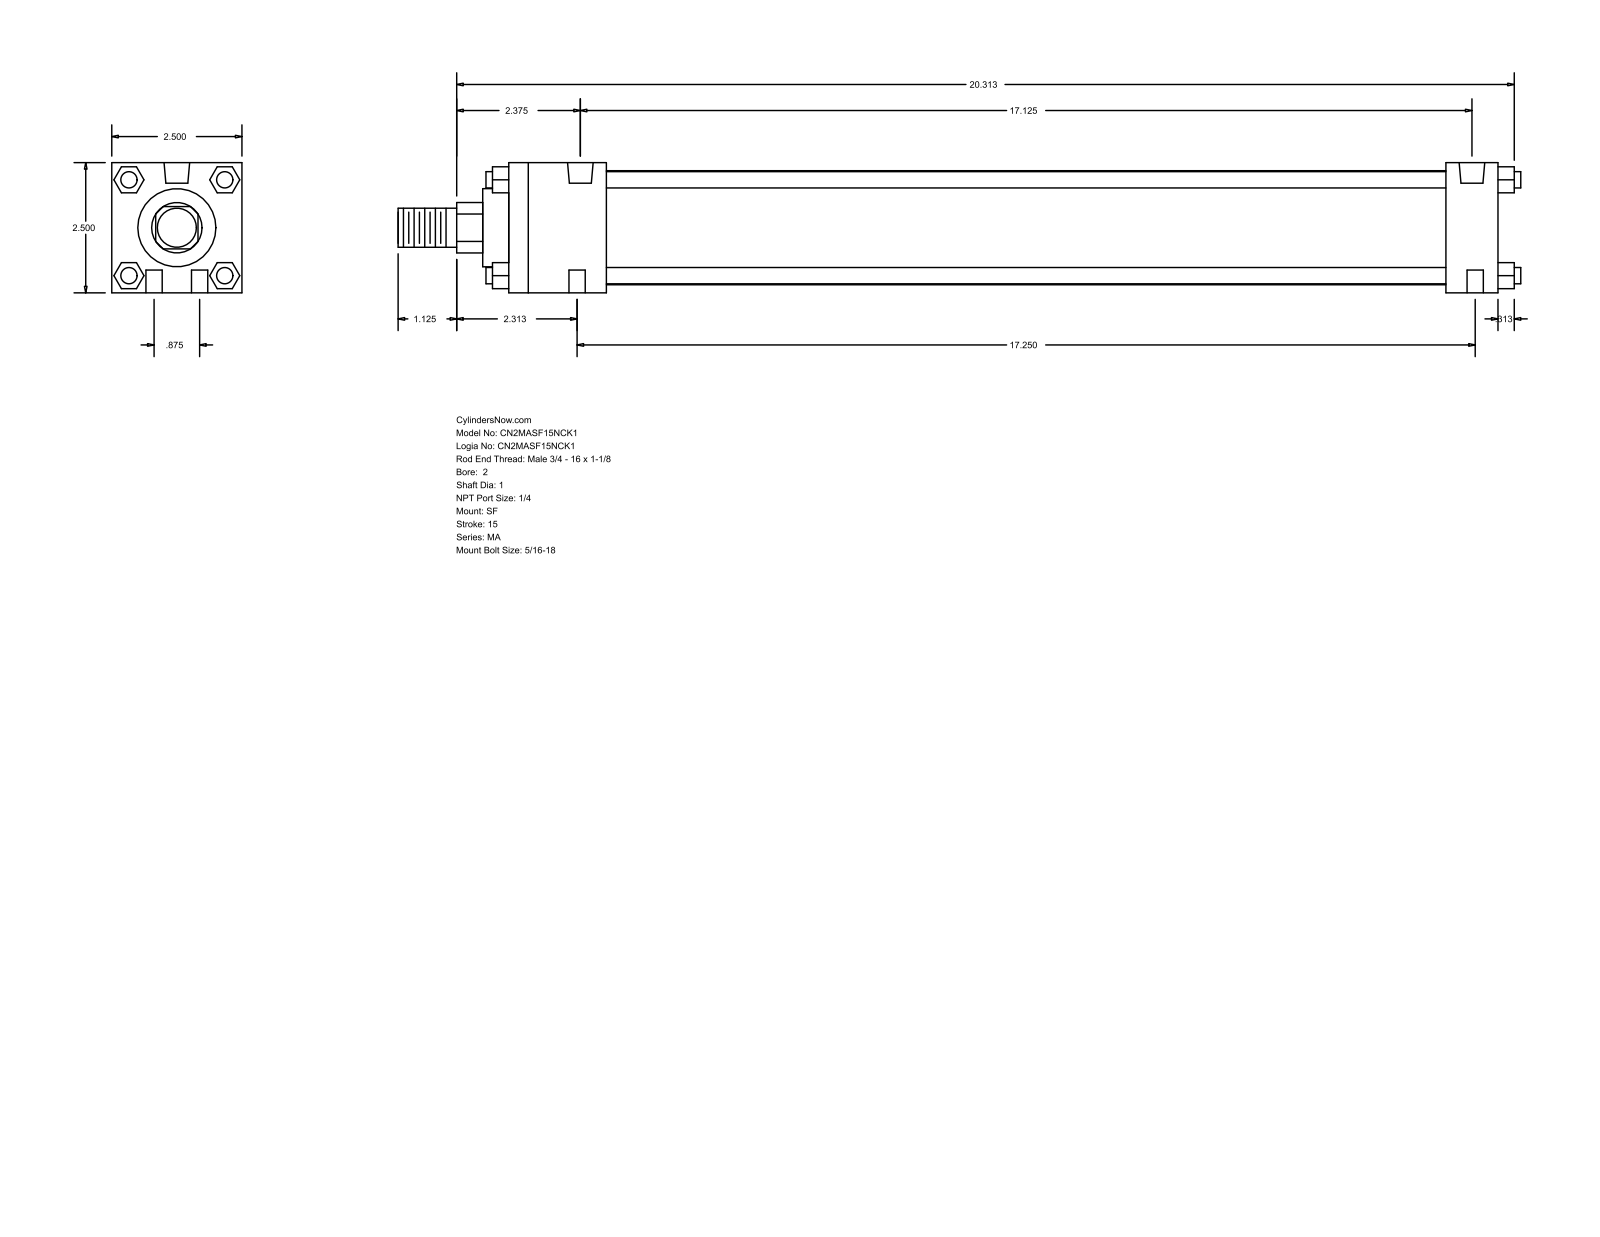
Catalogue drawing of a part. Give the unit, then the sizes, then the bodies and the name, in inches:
Units: inches
Overall size (bounding box): 21.563 × 2.5 × 2.5
Round holes (diameter × count): ⌀0.313 ×6, ⌀0.492 ×2
Round bosses / shafts (diameter × count): ⌀0.313 ×4, ⌀2.19 ×1, ⌀1.5 ×1, ⌀1 ×1, ⌀0.75 ×1
Partial cylindrical surfaces — rounded edges, fillets, slot ends (radius × count): R0.484 ×1
Main face-to-face distances: 2.5, 19, 0.5, 1, 18, 1.875, 16.125, 17.125, 0.92, 1.593
Hole centre spacings: 0.442, 17.193, 0.875, 17.125, 17.25, 17.272
Bodies: 0 solids, 124 faces (94 planar, 30 cylindrical, 0 other)
Part name (STEP PRODUCT): MA_SF__0200_1
STEP written by: GSSL Pune (CONFIG_CONTROL_DESIGN)
